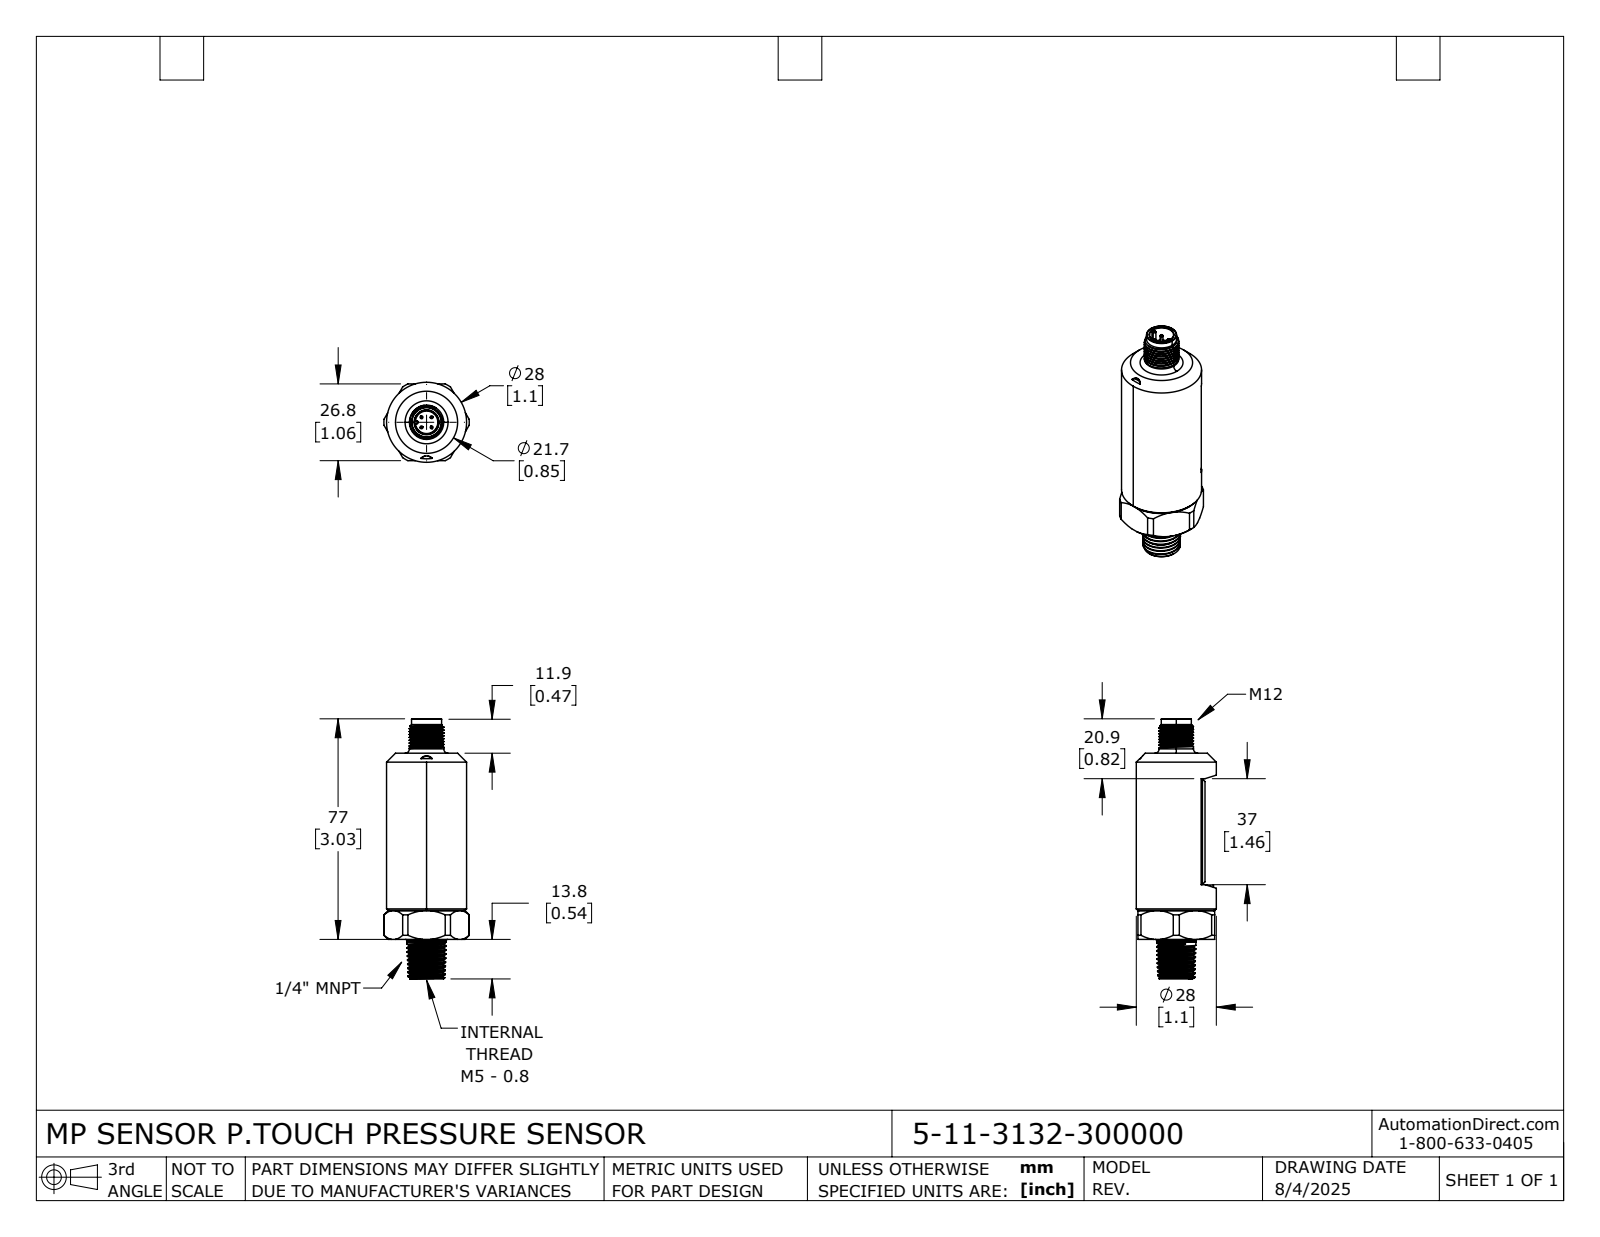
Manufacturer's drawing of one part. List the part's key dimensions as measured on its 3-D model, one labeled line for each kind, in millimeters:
Part name (STEP PRODUCT): 5-11-3132-300000
STEP written by: SolidWorks 2024 (AUTOMOTIVE_DESIGN)
Units: millimetres
Bodies: 1 solid, 199 faces (46 planar, 68 cylindrical, 85 other)
Overall size (bounding box): 90.8 × 29.8 × 27.9
Volume: 39 710 mm³ · Surface area: 8 916 mm²
Round holes (diameter × count): ⌀2 ×1, ⌀4.2 ×1, ⌀8.4 ×1
Round bosses / shafts (diameter × count): ⌀1 ×4, ⌀27.9 ×1, ⌀26 ×1, ⌀13.7 ×1, ⌀12 ×1, ⌀10.5 ×1
Partial cylindrical surfaces — rounded edges, fillets, slot ends (radius × count): R0.2 ×2, R2.3 ×1, R14.9 ×1
Main face-to-face distances: 26.8, 65, 23.4, 3.4, 13.8, 78.8, 9, 46, 8.9, 4.7
